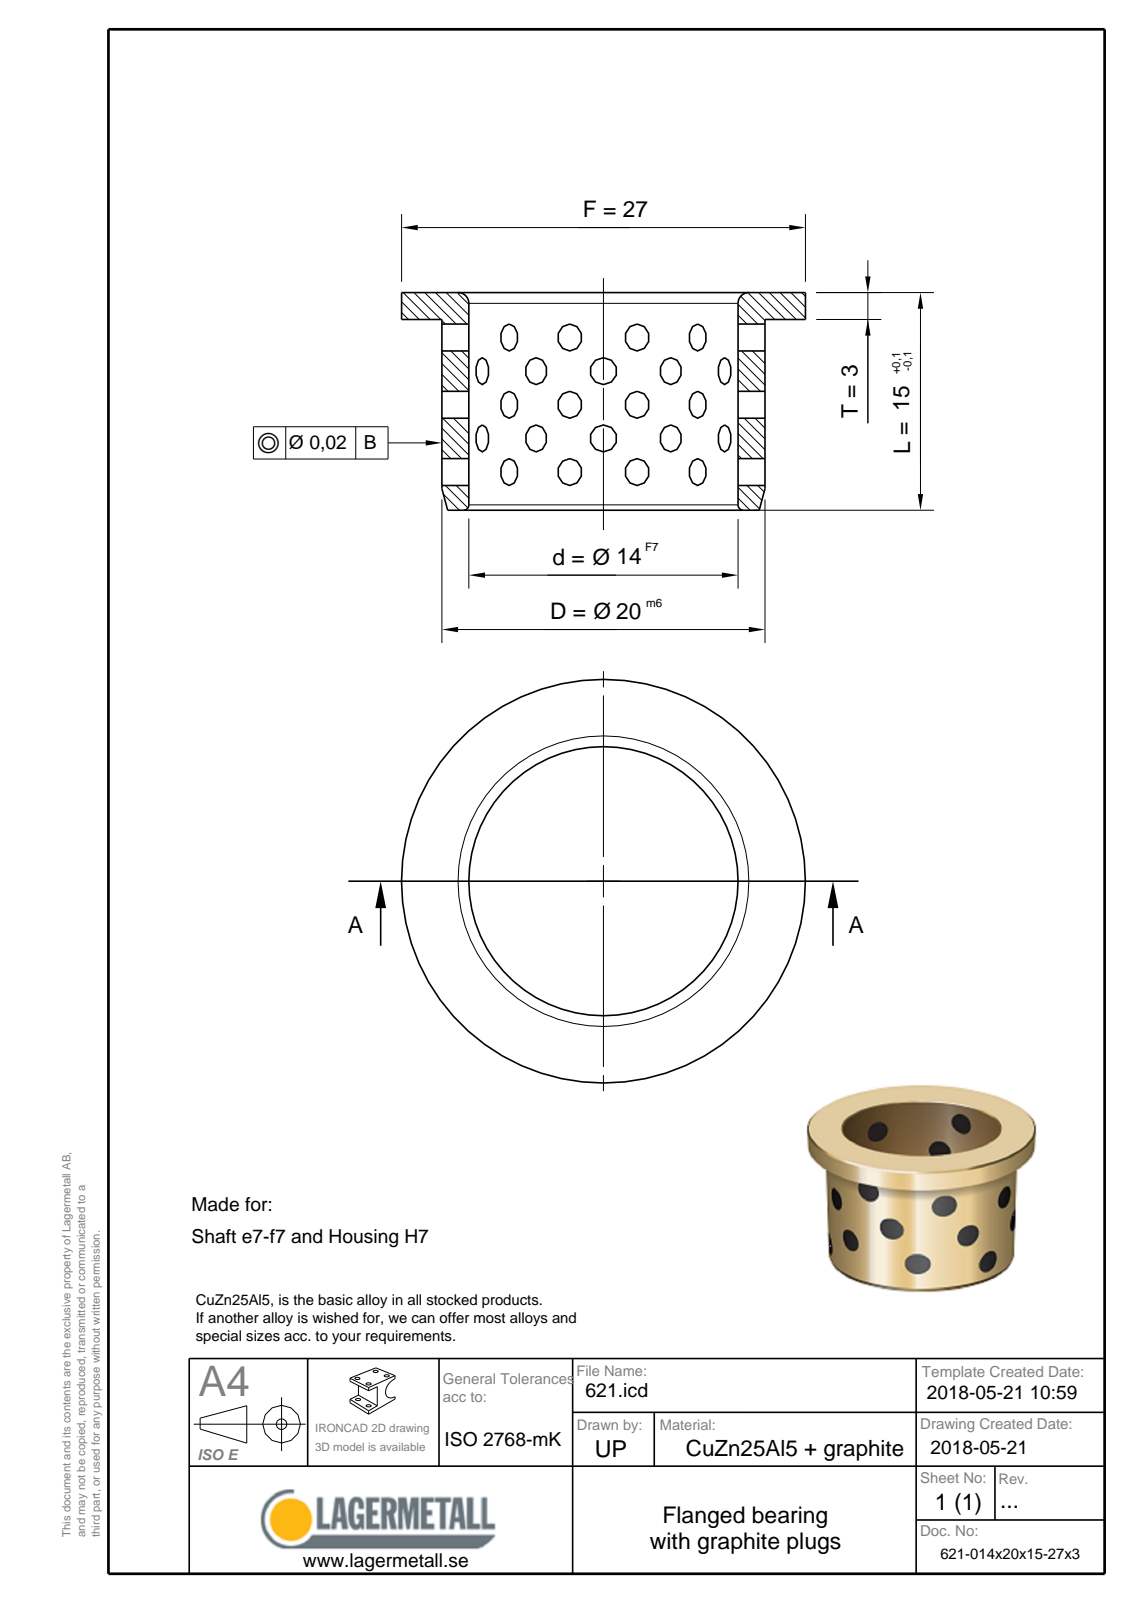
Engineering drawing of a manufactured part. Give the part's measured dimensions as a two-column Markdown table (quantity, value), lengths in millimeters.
| quantity | value |
| --- | --- |
| part name | 621-014x20x15-27x3 |
| STEP written by | Spatial InterOp 3D (CONFIG_CONTROL_DESIGN) |
| units | millimeters |
| bodies | 1 solid, 9 faces (3 planar, 3 cylindrical, 3 other) |
| overall size | 27 × 27 × 15 |
| volume | 3 090 mm³ |
| surface area | 2 408 mm² |
| round holes (diameter × count) | 14 × 1 |
| round bosses / shafts (diameter × count) | 27 × 1, 20 × 1 |
| main face-to-face distances | 3, 12, 15 |
